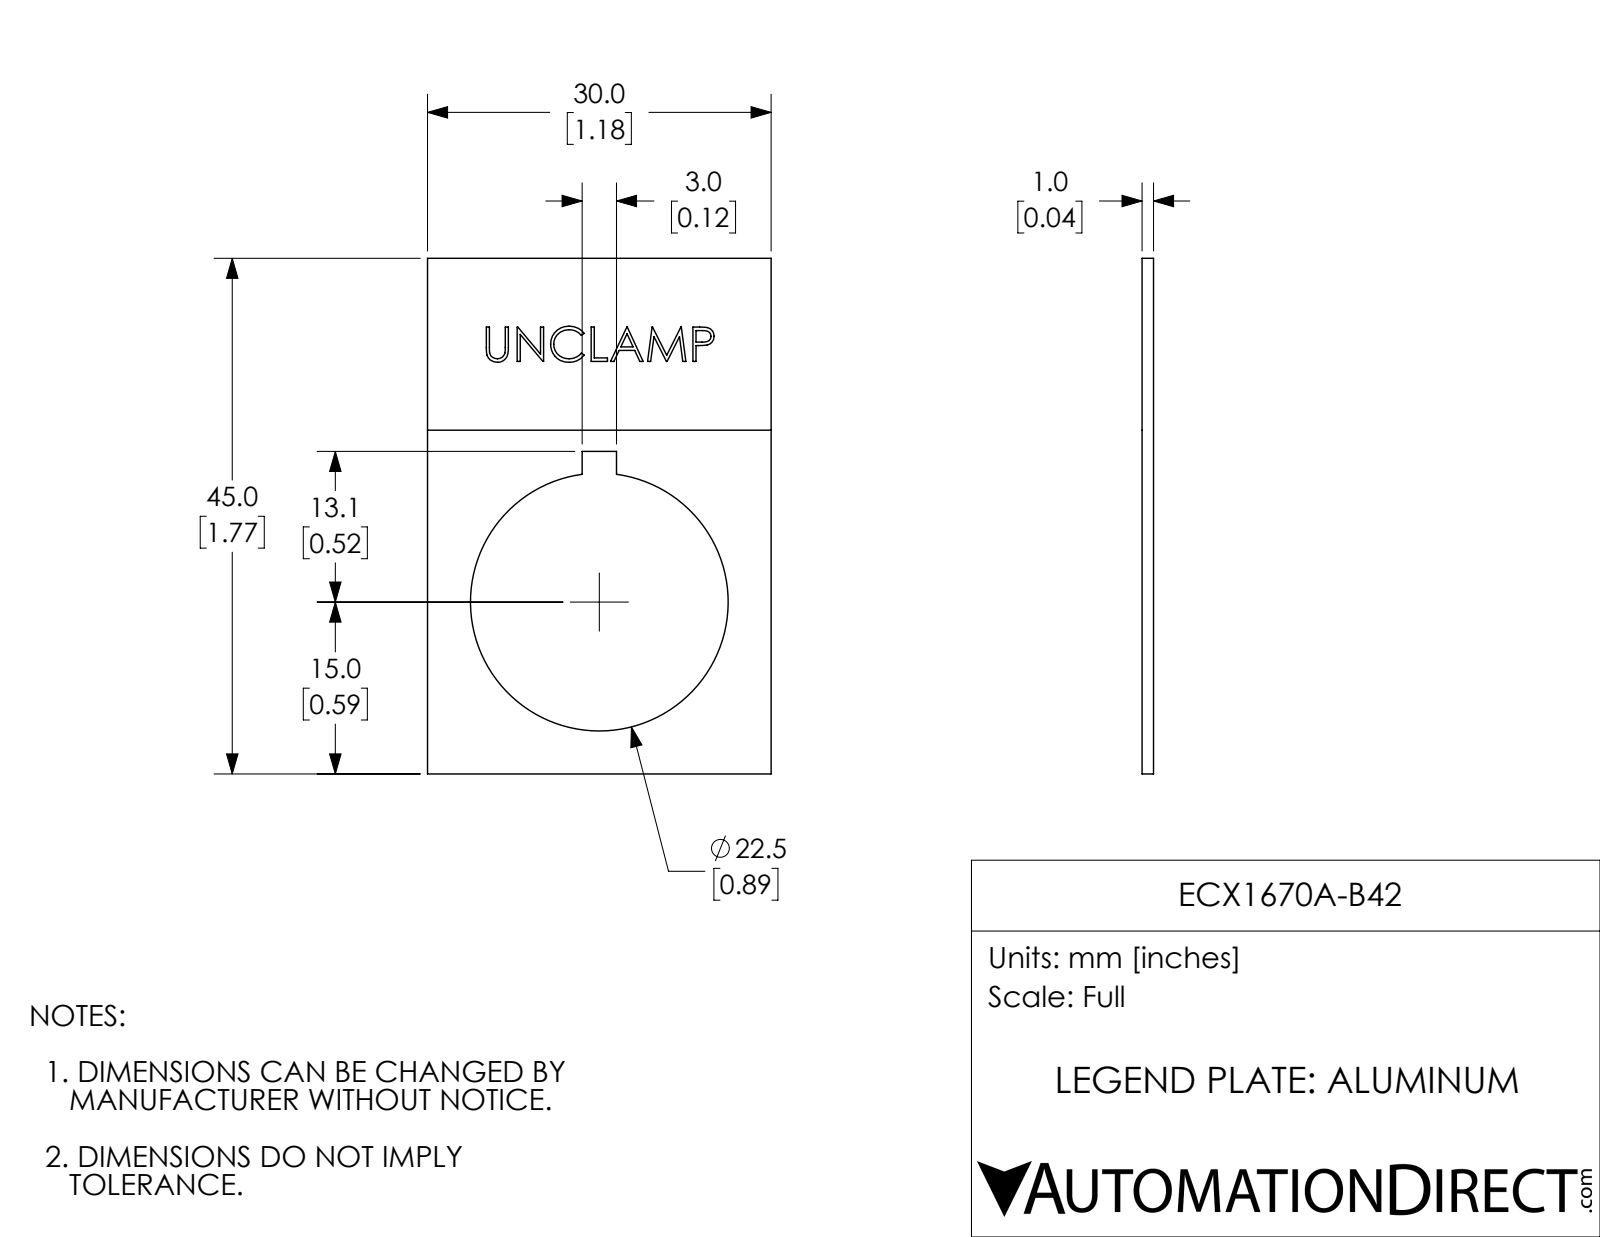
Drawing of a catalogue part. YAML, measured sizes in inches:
part_name: "ECX1670A-B42"
step_written_by: "SolidWorks 2017 (AUTOMOTIVE_DESIGN)"
units: inches
bodies: {solids: 1, faces: 100, planar: 75, cylindrical: 3, other: 22}
overall_size: [1.772, 1.181, 0.039]
volume: 0.058
surface_area: 3.287
round_holes:
  - {diameter: 0.886, count: 1}
face_to_face_distances: [0.039, 1.181, 1.772, 0.038, 0.531, 0.65, 1.108, 0.663, 0.118, 0.35]
